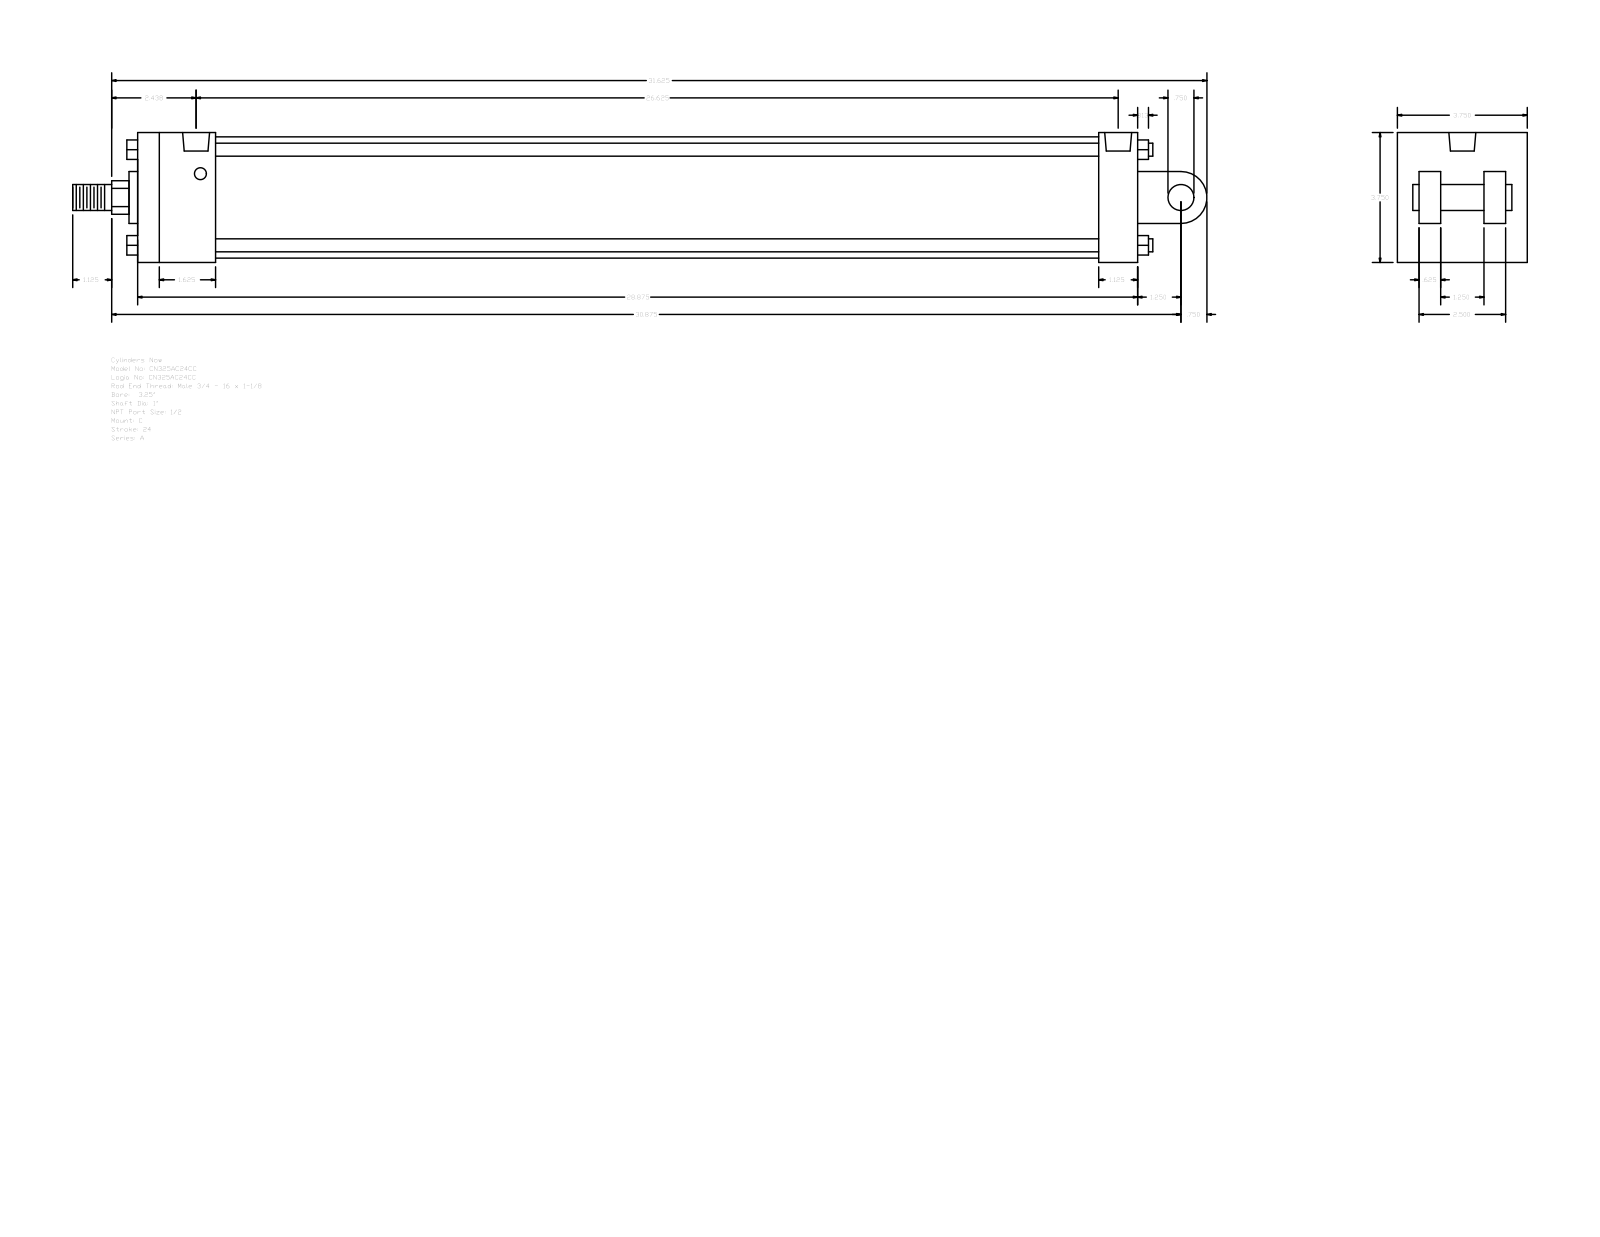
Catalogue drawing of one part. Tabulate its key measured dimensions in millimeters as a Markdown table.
| quantity | value |
| --- | --- |
| part name | A_C__0325_1 |
| STEP written by | GSSL Pune (CONFIG_CONTROL_DESIGN) |
| units | millimeters |
| bodies | 0 solids, 135 faces (102 planar, 33 cylindrical, 0 other) |
| overall size | 831.85 × 95.25 × 95.25 |
| round holes (diameter × count) | 8.73 × 4, 19.77 × 2 |
| round bosses / shafts (diameter × count) | 9.53 × 4, 19.05 × 2, 88.9 × 1, 38.1 × 1, 25.4 × 1 |
| partial cylindrical surfaces (radius × count) | 12.29 × 1, 19.05 × 1 |
| main face-to-face distances | 95.24, 733.43, 15.87, 63.5, 31.74, 79.37, 47.63, 66.67, 704.85, 28.58 |
| hole center spacings | 3.18, 669.92, 673.1, 676.28 |
